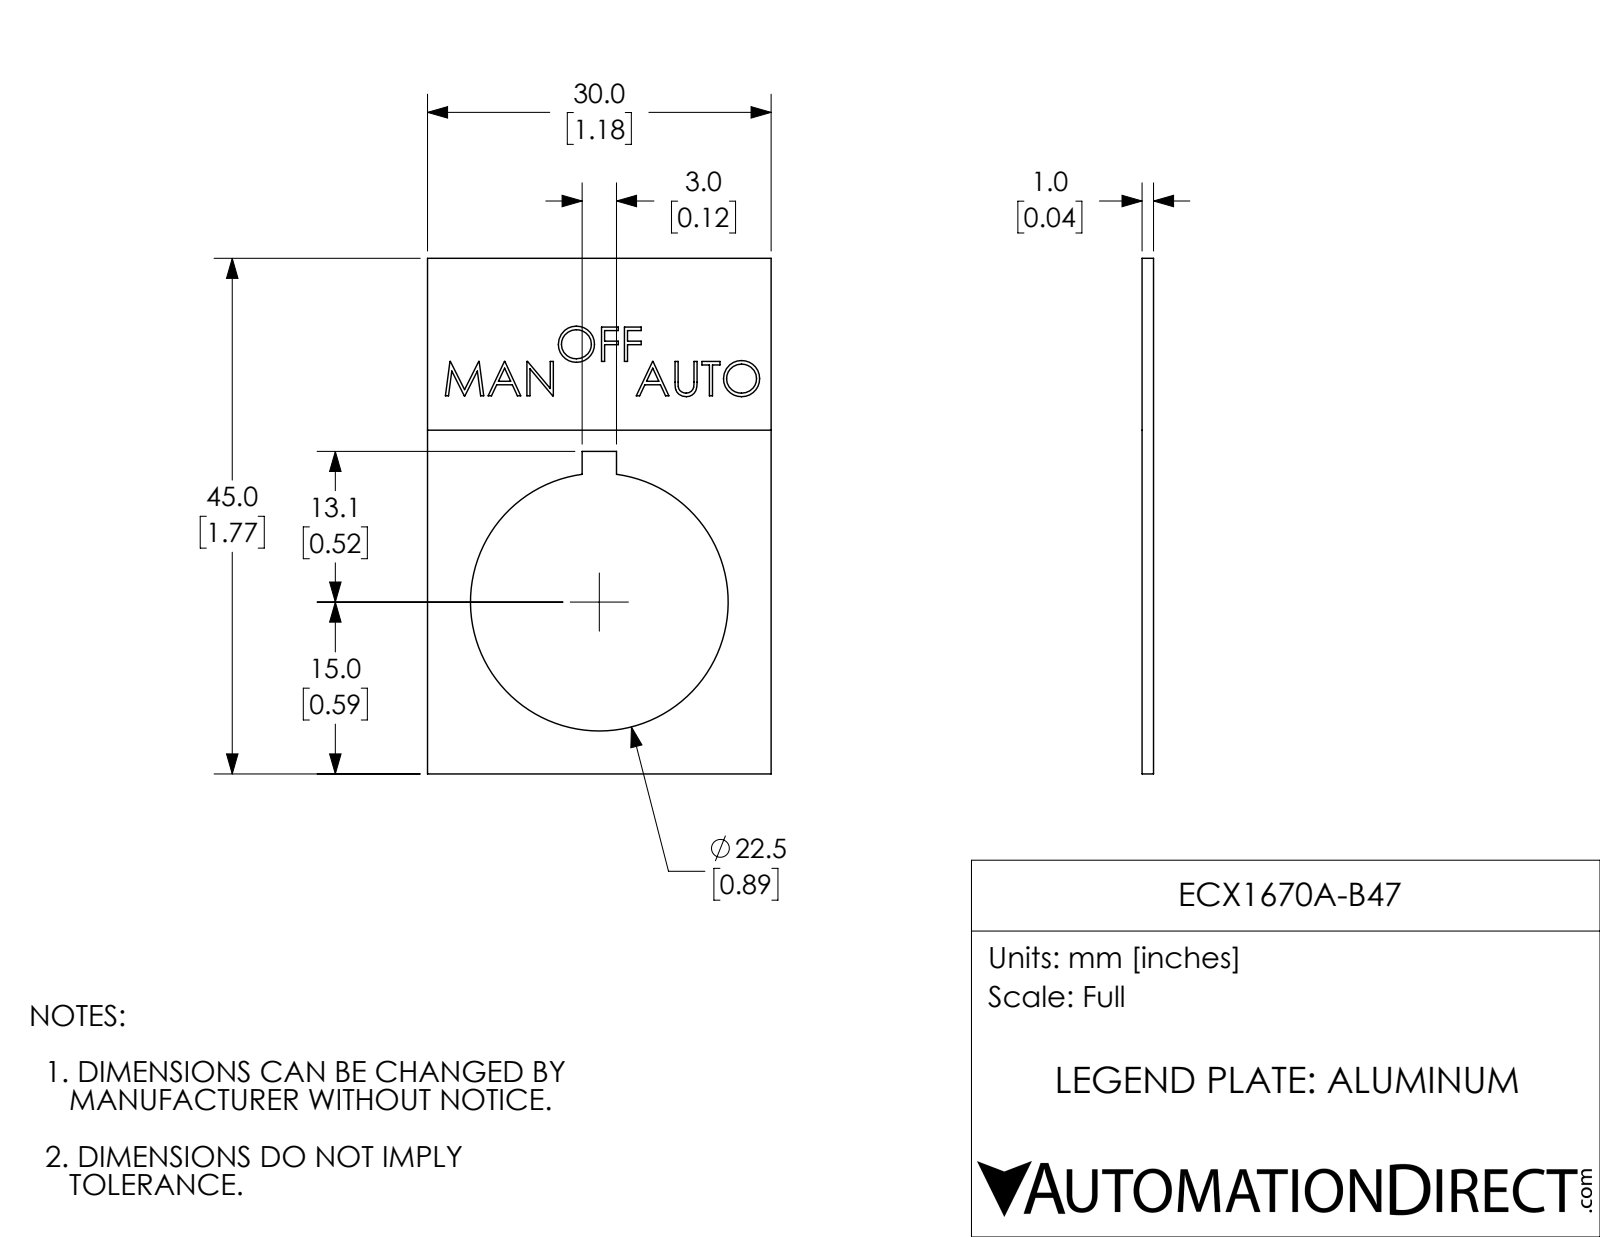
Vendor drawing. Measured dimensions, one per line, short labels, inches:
name: ECX1670A-B47
written by: SolidWorks 2017 (AUTOMOTIVE_DESIGN)
unit: in
bodies: 1 solid, 129 faces (103 planar, 3 cylindrical, 23 other)
size: 1.772 × 1.181 × 0.039
volume: 0.058 in³; area: 3.289 in²
holes: 1× ⌀0.886
face distances: 0.039, 1.181, 1.772, 0.038, 0.531, 0.65, 1.108, 0.663, 0.118, 0.012
